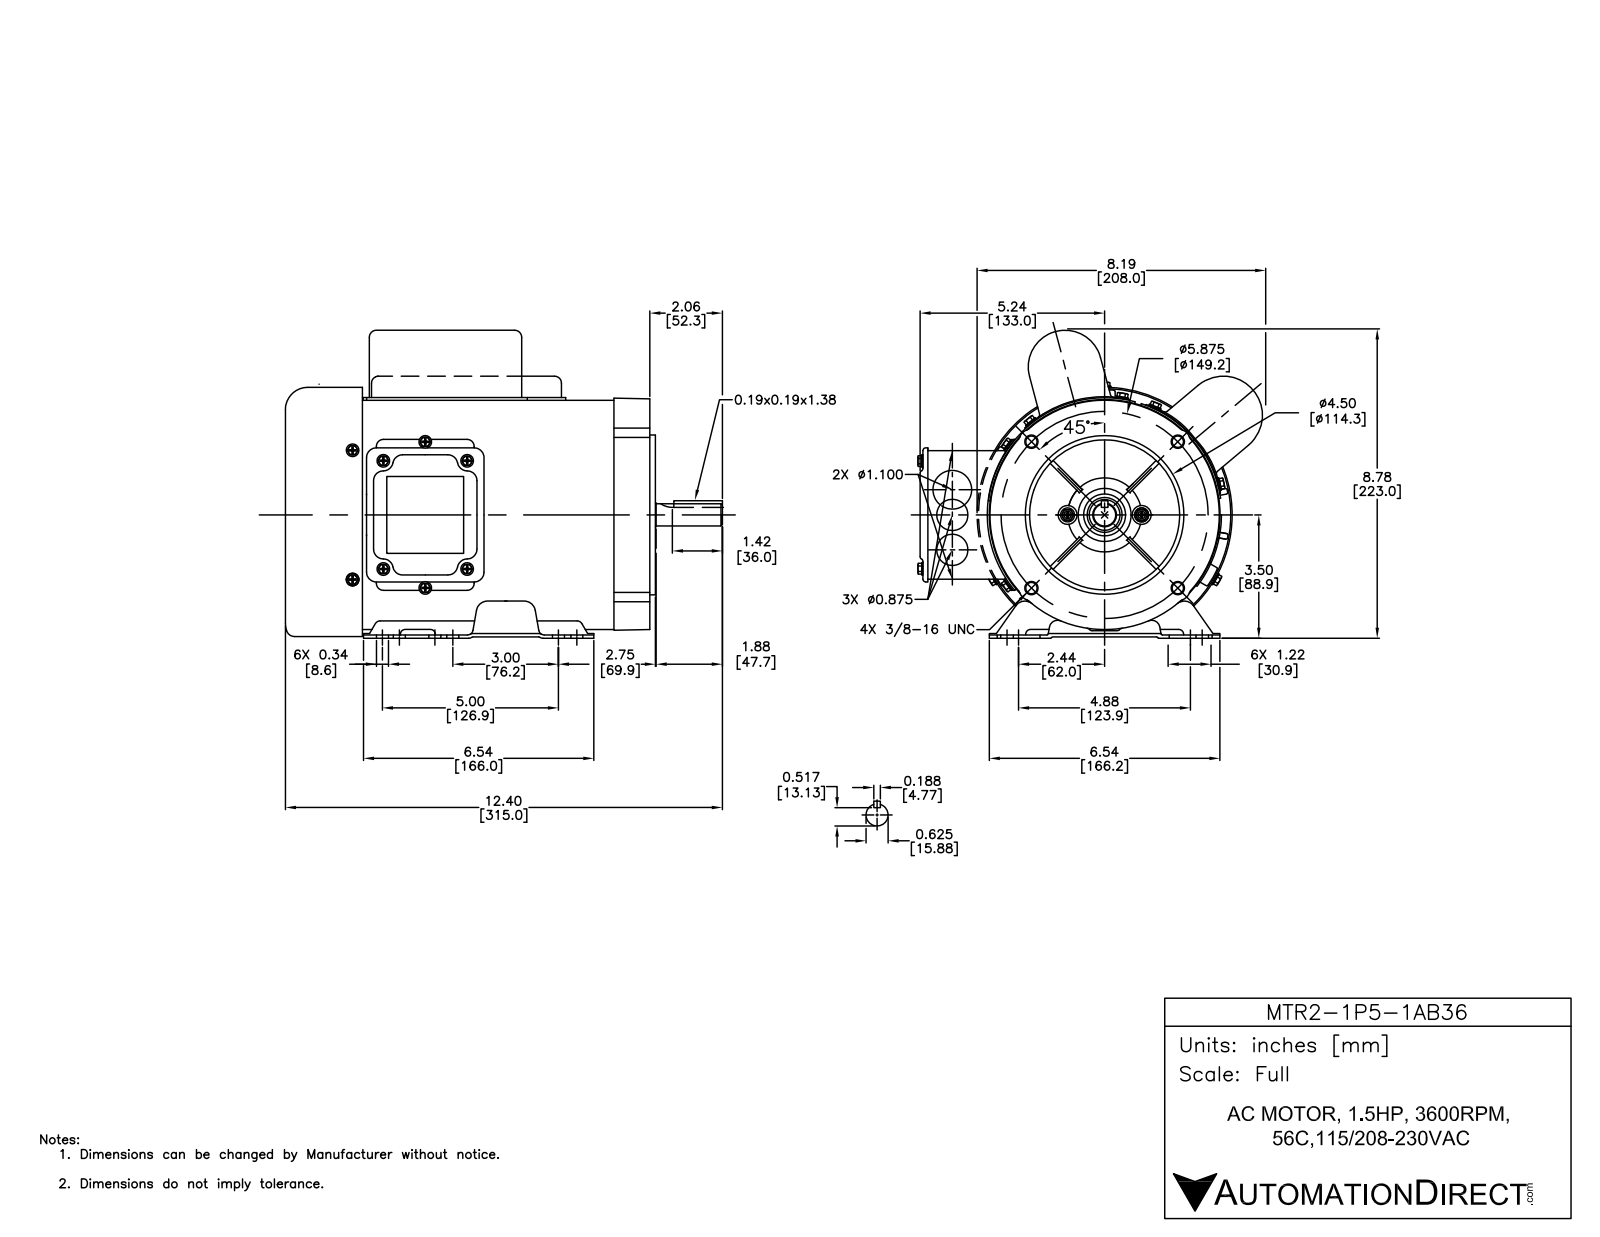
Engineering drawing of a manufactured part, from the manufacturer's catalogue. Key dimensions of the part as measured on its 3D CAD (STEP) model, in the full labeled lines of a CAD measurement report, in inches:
Part name (STEP PRODUCT): MTR2-1P5-1AB36
STEP written by: SolidWorks 2015 (AUTOMOTIVE_DESIGN)
Units: inches
Bodies: 0 solids, 1389 faces (533 planar, 582 cylindrical, 274 other)
Overall size (bounding box): 12.4 × 10.024 × 9.782
Round holes (diameter × count): ⌀0.219 ×13, ⌀0.248 ×6, ⌀0.344 ×6, ⌀0.313 ×4, ⌀0.273 ×2, ⌀0.276 ×2, ⌀0.512 ×2, ⌀0.124 ×1, ⌀0.315 ×1, ⌀1.142 ×1, ⌀4.213 ×1, ⌀7.106 ×1
Round bosses / shafts (diameter × count): ⌀0.348 ×13, ⌀6.457 ×2, ⌀0.551 ×2, ⌀0.414 ×2, ⌀0.164 ×2, ⌀7.185 ×1, ⌀6.496 ×1, ⌀6.456 ×1
Partial cylindrical surfaces — rounded edges, fillets, slot ends (radius × count): R0.118 ×98, R0.039 ×25, R0.075 ×23, R0.197 ×19, R0.1 ×16, R0.276 ×16, R0.228 ×14, R0.315 ×14
Main face-to-face distances: 0.075, 1.388, 10.341, 8.953, 0.043, 0.118, 1.33, 0.058, 9.011, 0.039
Hole centre spacings: 2.937, 3.748, 5.5, 1, 1.043, 2.32, 2.362, 3.346
